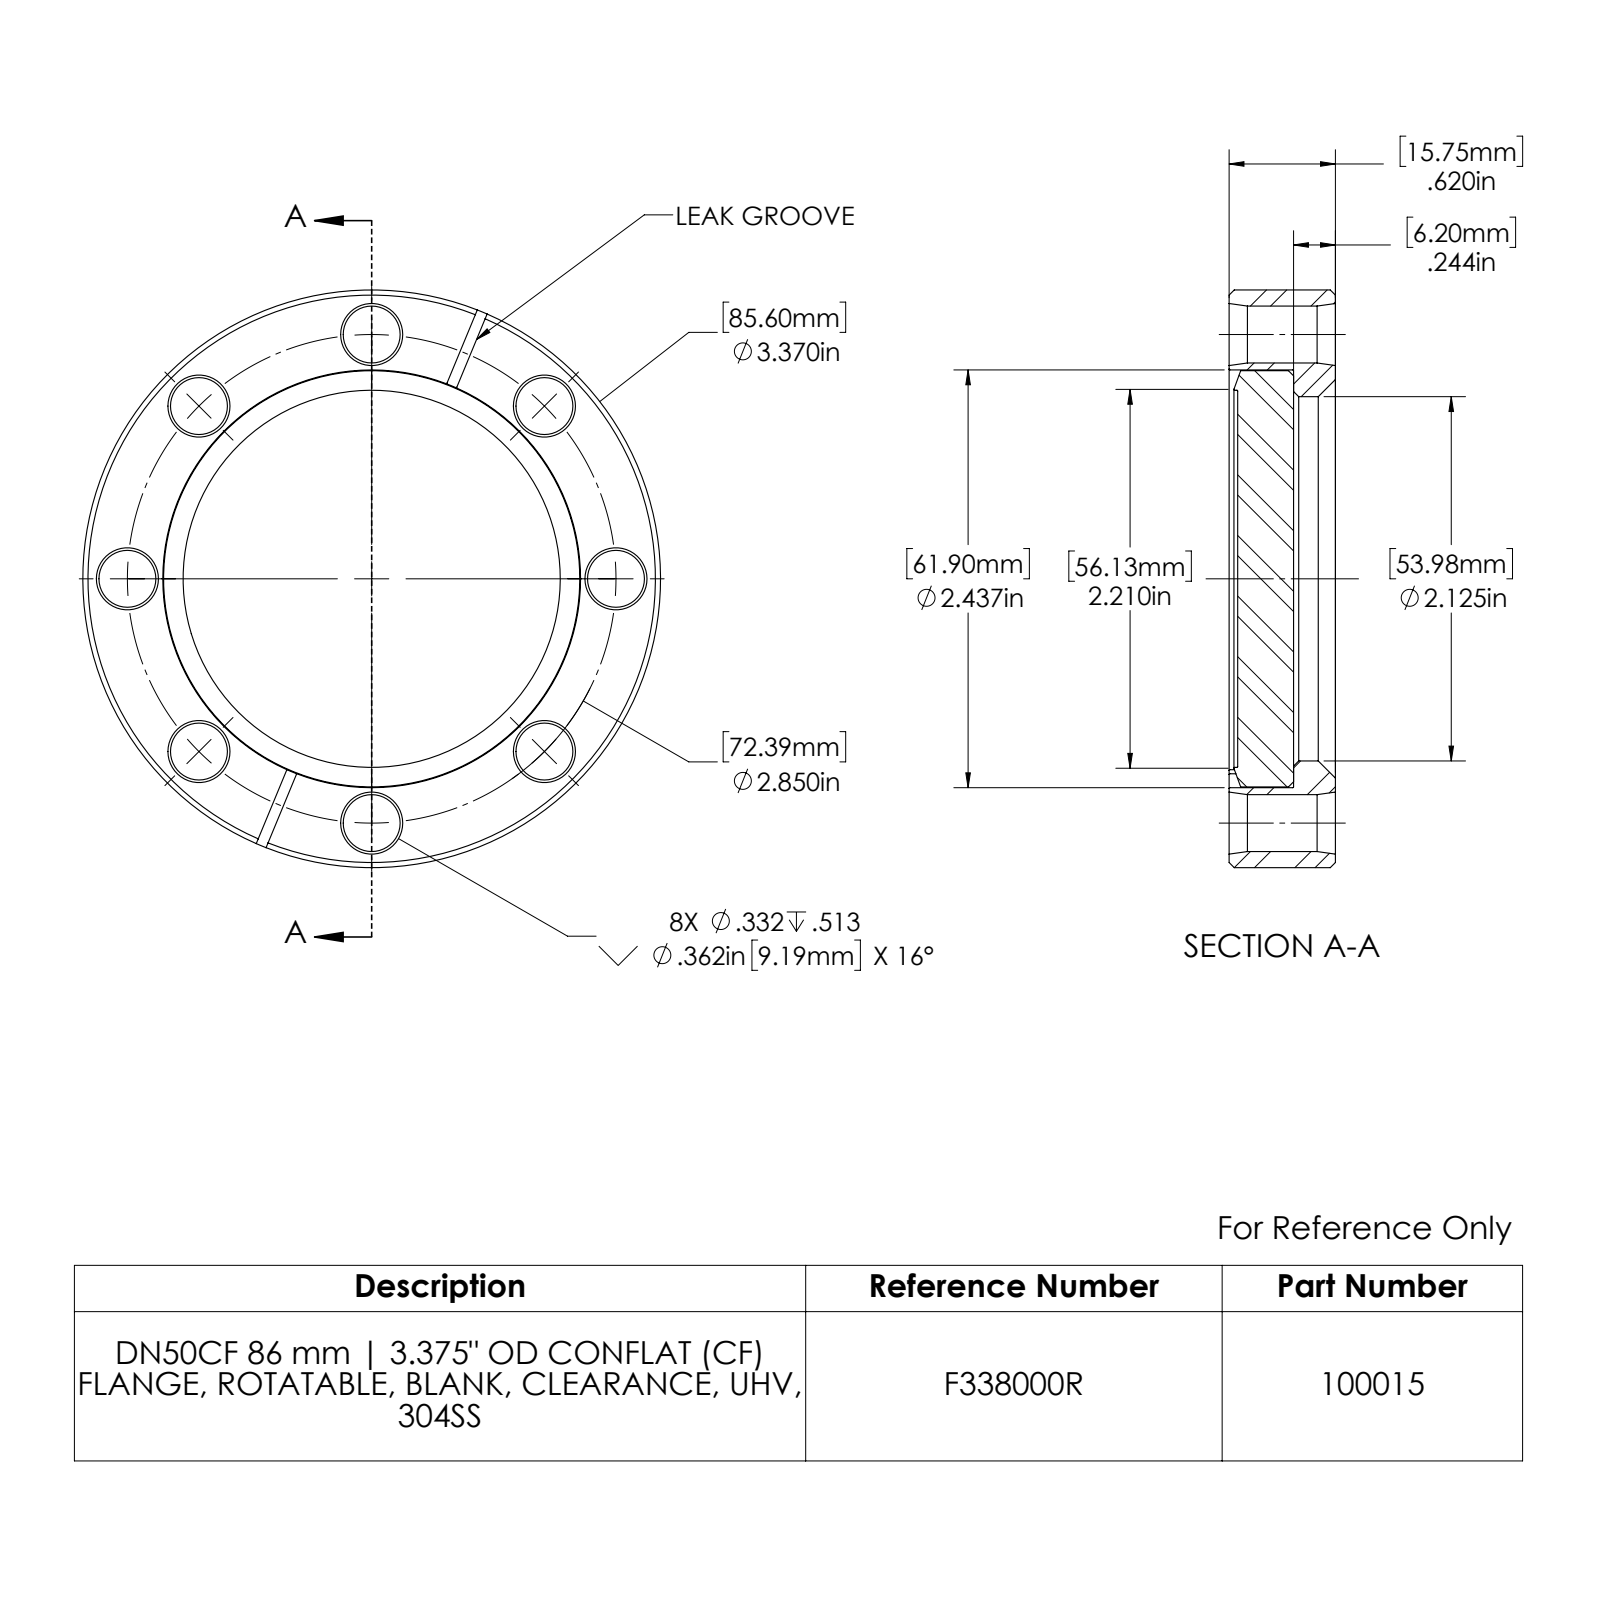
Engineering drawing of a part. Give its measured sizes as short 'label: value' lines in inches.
name: 100015_A; 910015; 915003
written by: SolidWorks 2022 (CONFIG_CONTROL_DESIGN)
unit: in
bodies: 2 solids, 92 faces (12 planar, 26 cylindrical, 54 other)
size: 3.37 × 3.37 × 0.62
volume: 3.926 in³; area: 36.29 in²
holes: 8× ⌀0.332, 1× ⌀2.125, 1× ⌀2.2, 1× ⌀2.437
bosses: 1× ⌀3.37, 1× ⌀2.428
face distances: 0.326, 0.57, 0.244, 0.05, 0.376, 0.62, 0.062, 0.012, 0.314, 0.558
hole spacings: 2.633, 2.015, 1.425, 1.091, 1.091, 2.85, 1.425, 2.015
